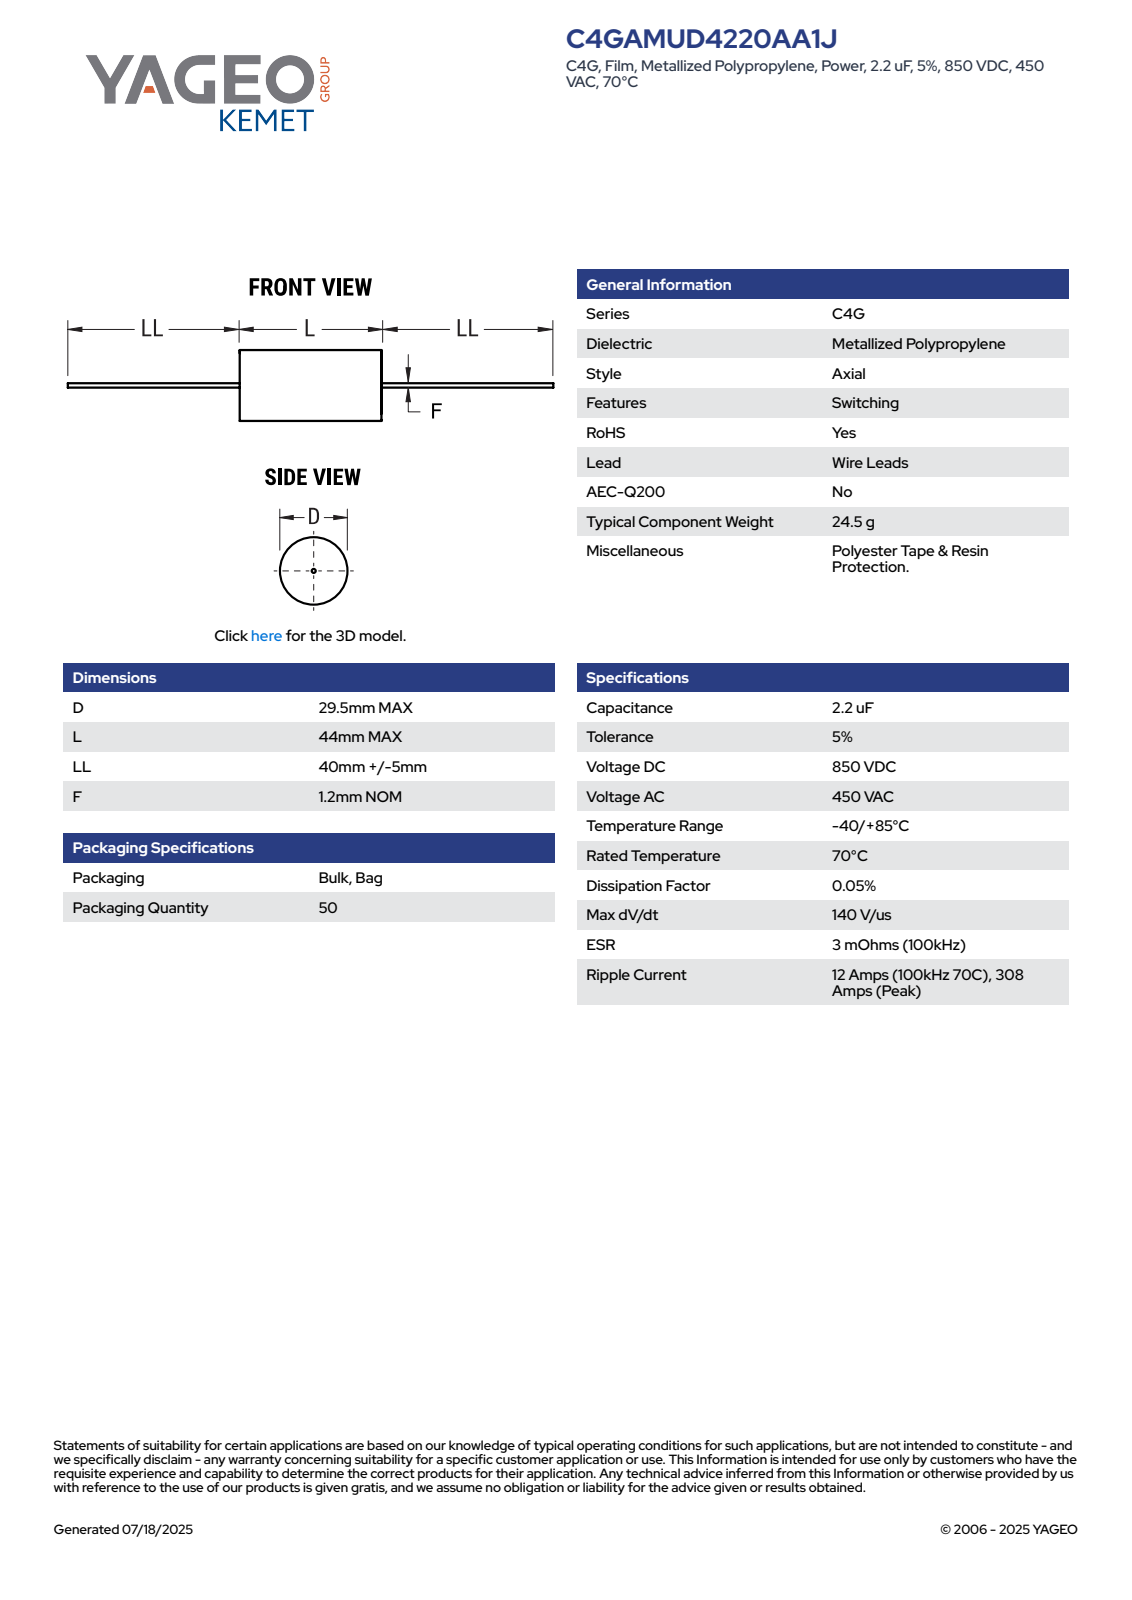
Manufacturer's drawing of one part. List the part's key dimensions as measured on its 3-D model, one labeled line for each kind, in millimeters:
Part name (STEP PRODUCT): CFP_ACWF_29.5X44_D29.5L44LL45F1.2
STEP written by: SolidWorks 2014 (AUTOMOTIVE_DESIGN)
Units: millimetres
Bodies: 2 solids, 87 faces (28 planar, 28 cylindrical, 31 other)
Overall size (bounding box): 134 × 29.5 × 29.5
Volume: 30 175 mm³ · Surface area: 7 150 mm²
Round bosses / shafts (diameter × count): ⌀29.5 ×1, ⌀1.2 ×1
Partial cylindrical surfaces — rounded edges, fillets, slot ends (radius × count): R14.74 ×1
Main face-to-face distances: 44, 43.99, 44.99, 45, 88.99, 134, 89.01, 89, 45.01
